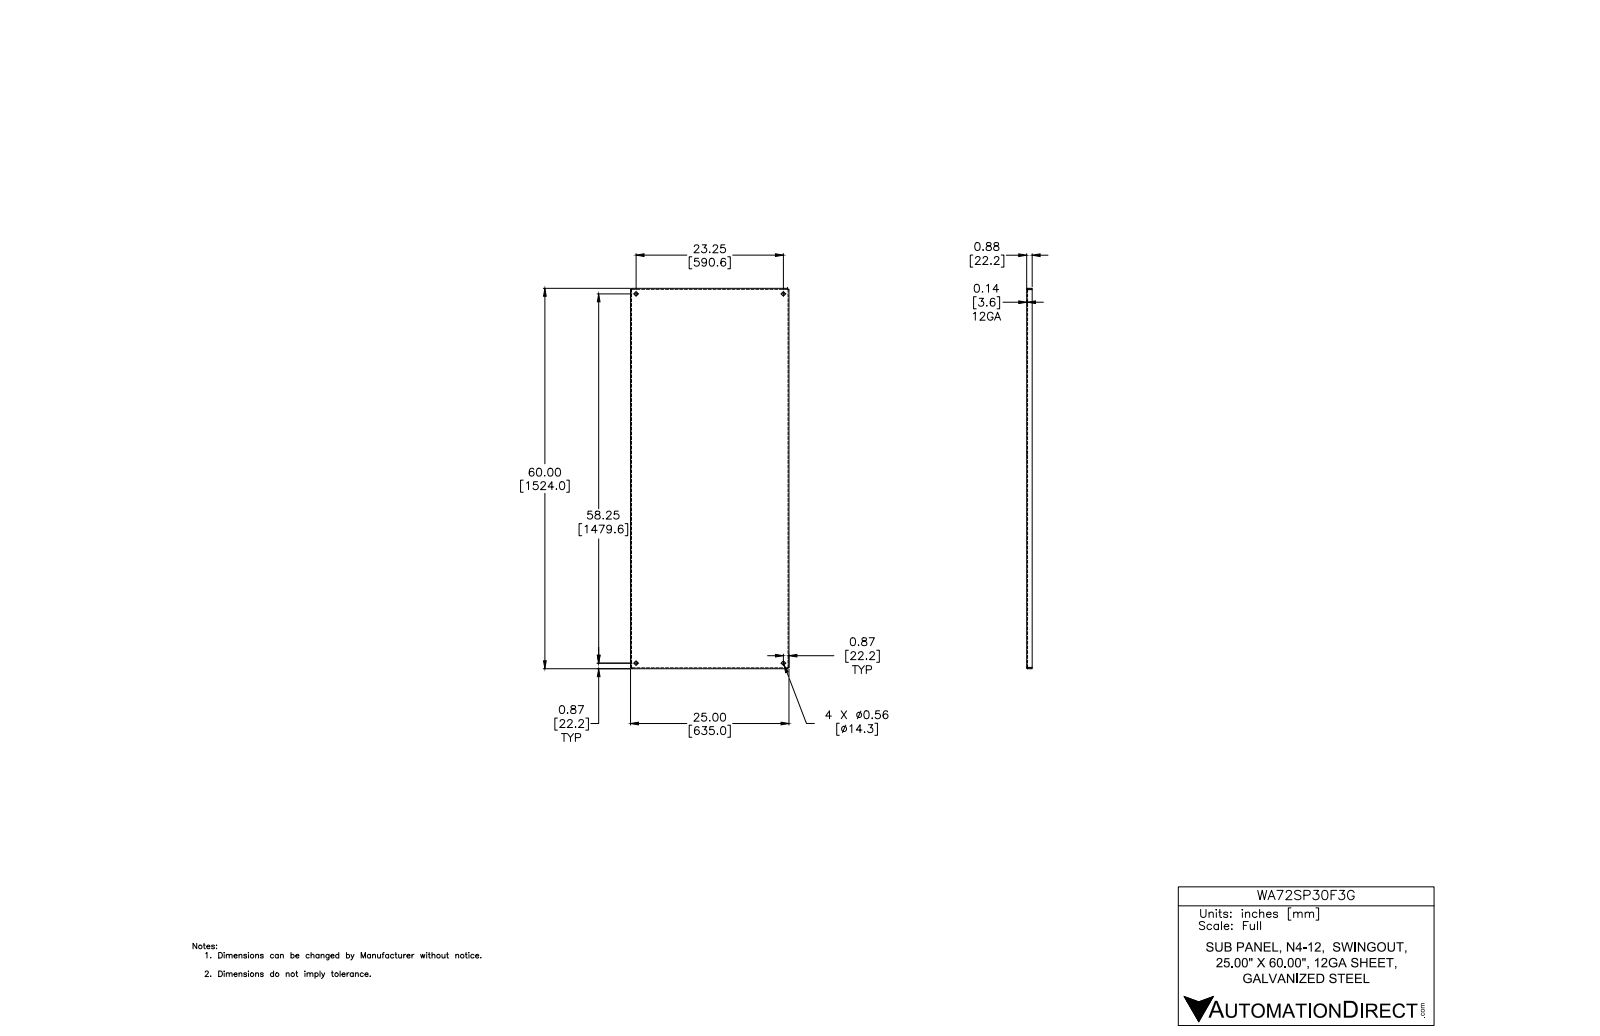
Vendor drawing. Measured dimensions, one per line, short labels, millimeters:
name: WA60SP24F3G-WA90SP36F4G
written by: Autodesk Inventor 2012 (AUTOMOTIVE_DESIGN)
unit: mm
bodies: 1 solid, 42 faces (22 planar, 12 cylindrical, 8 other)
size: 1524 × 635 × 22.2
volume: 2 497 000 mm³; area: 2 108 000 mm²
holes: 4× ⌀14.3
rounds: 4× R0.8, 4× R3.2
face distances: 2.4, 632.6, 635, 630.3, 1521.6, 1524, 1519.3, 19.8, 22.2, 4.1
hole spacings: 590.6, 1479.6, 1593.1
